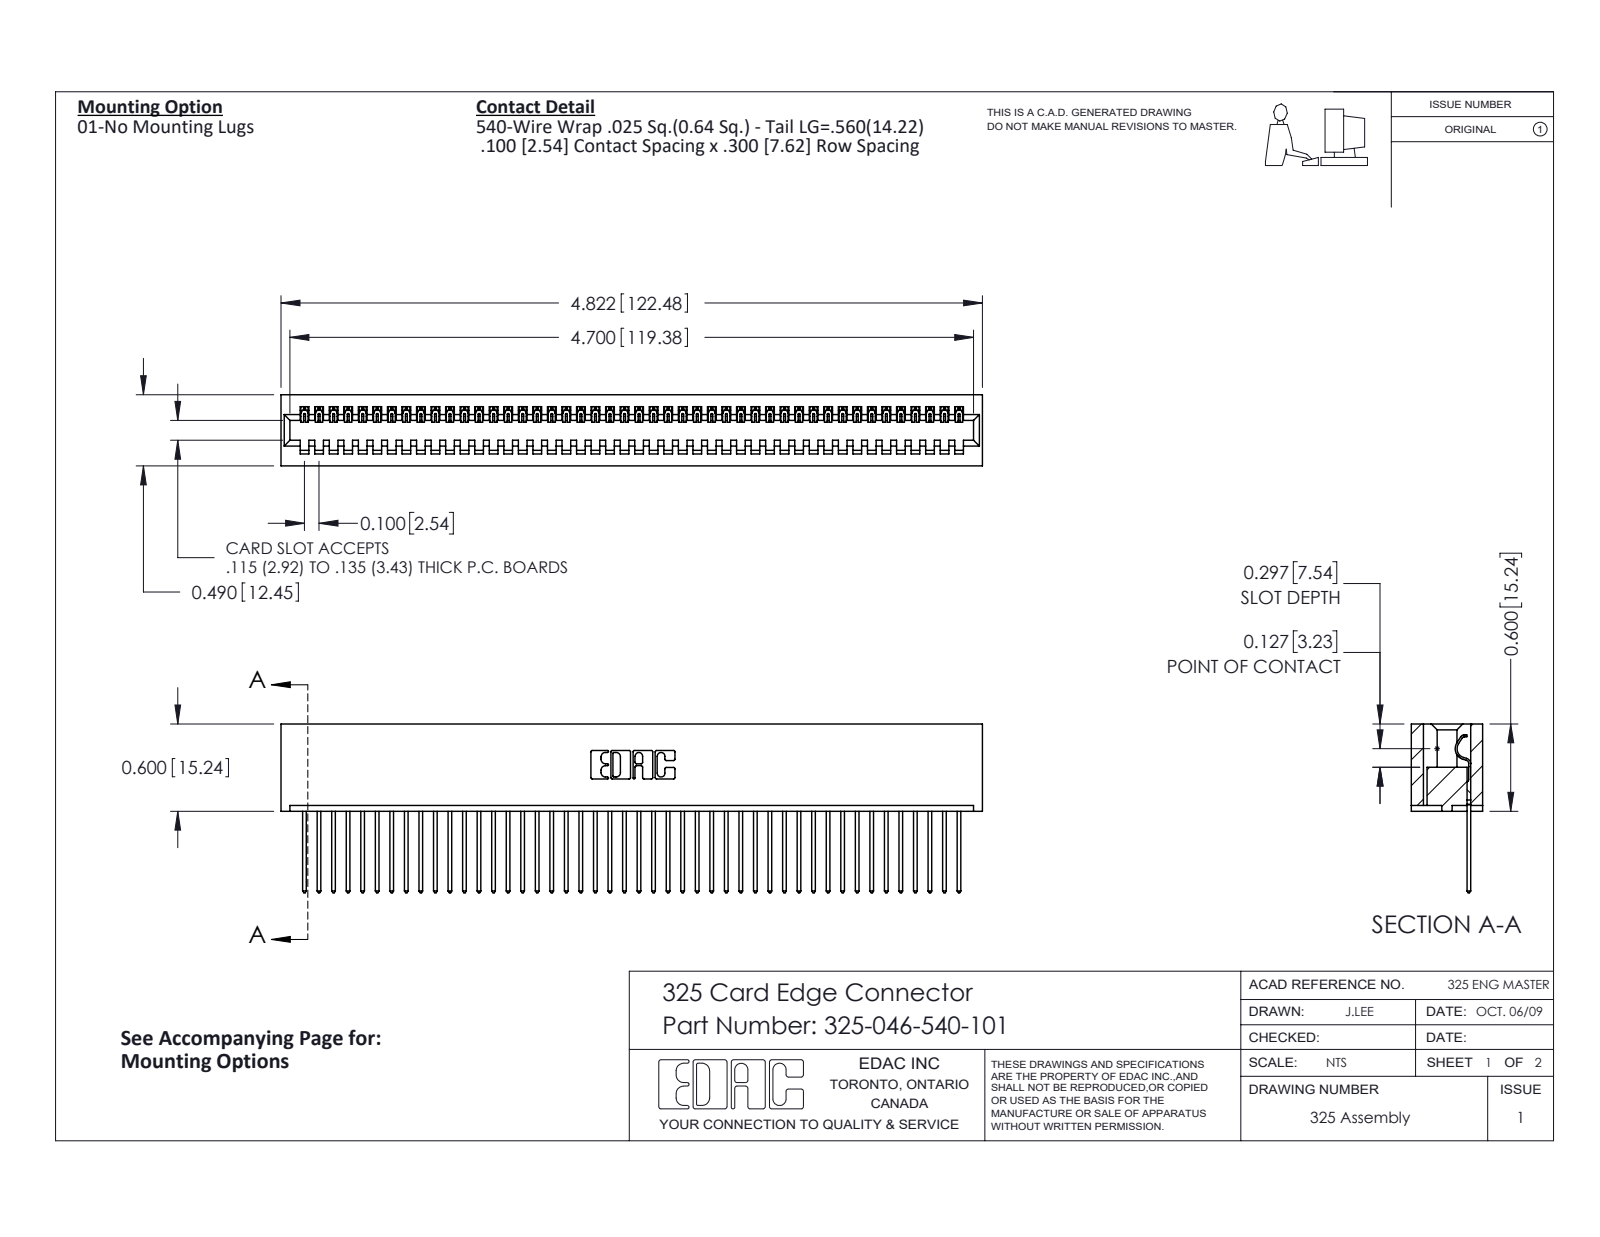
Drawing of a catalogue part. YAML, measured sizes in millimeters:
part_name: "325-292-001_325-293-140; 325-046-540-101; 325 Part_Lugless"
step_written_by: "SolidWorks 2016 (CONFIG_CONTROL_DESIGN)"
units: millimeters
bodies: {solids: 47, faces: 2774, planar: 1998, cylindrical: 776, other: 0}
overall_size: [122.5, 29.5, 12.4]
volume: 16200
surface_area: 18740
partial_cylinders:
  - {radius: 0.2, count: 92}
  - {radius: 0.3, count: 92}
  - {radius: 0.3, count: 22}
  - {radius: 0.2, count: 6}
  - {radius: 0.8, count: 6}
  - {radius: 0.7, count: 3}
  - {radius: 0.4, count: 1}
  - {radius: 0.6, count: 1}
face_to_face_distances: [2.1, 10.3, 12.4, 7.6, 2.7, 9.7, 0.6, 8.3, 14.2, 6.7]
